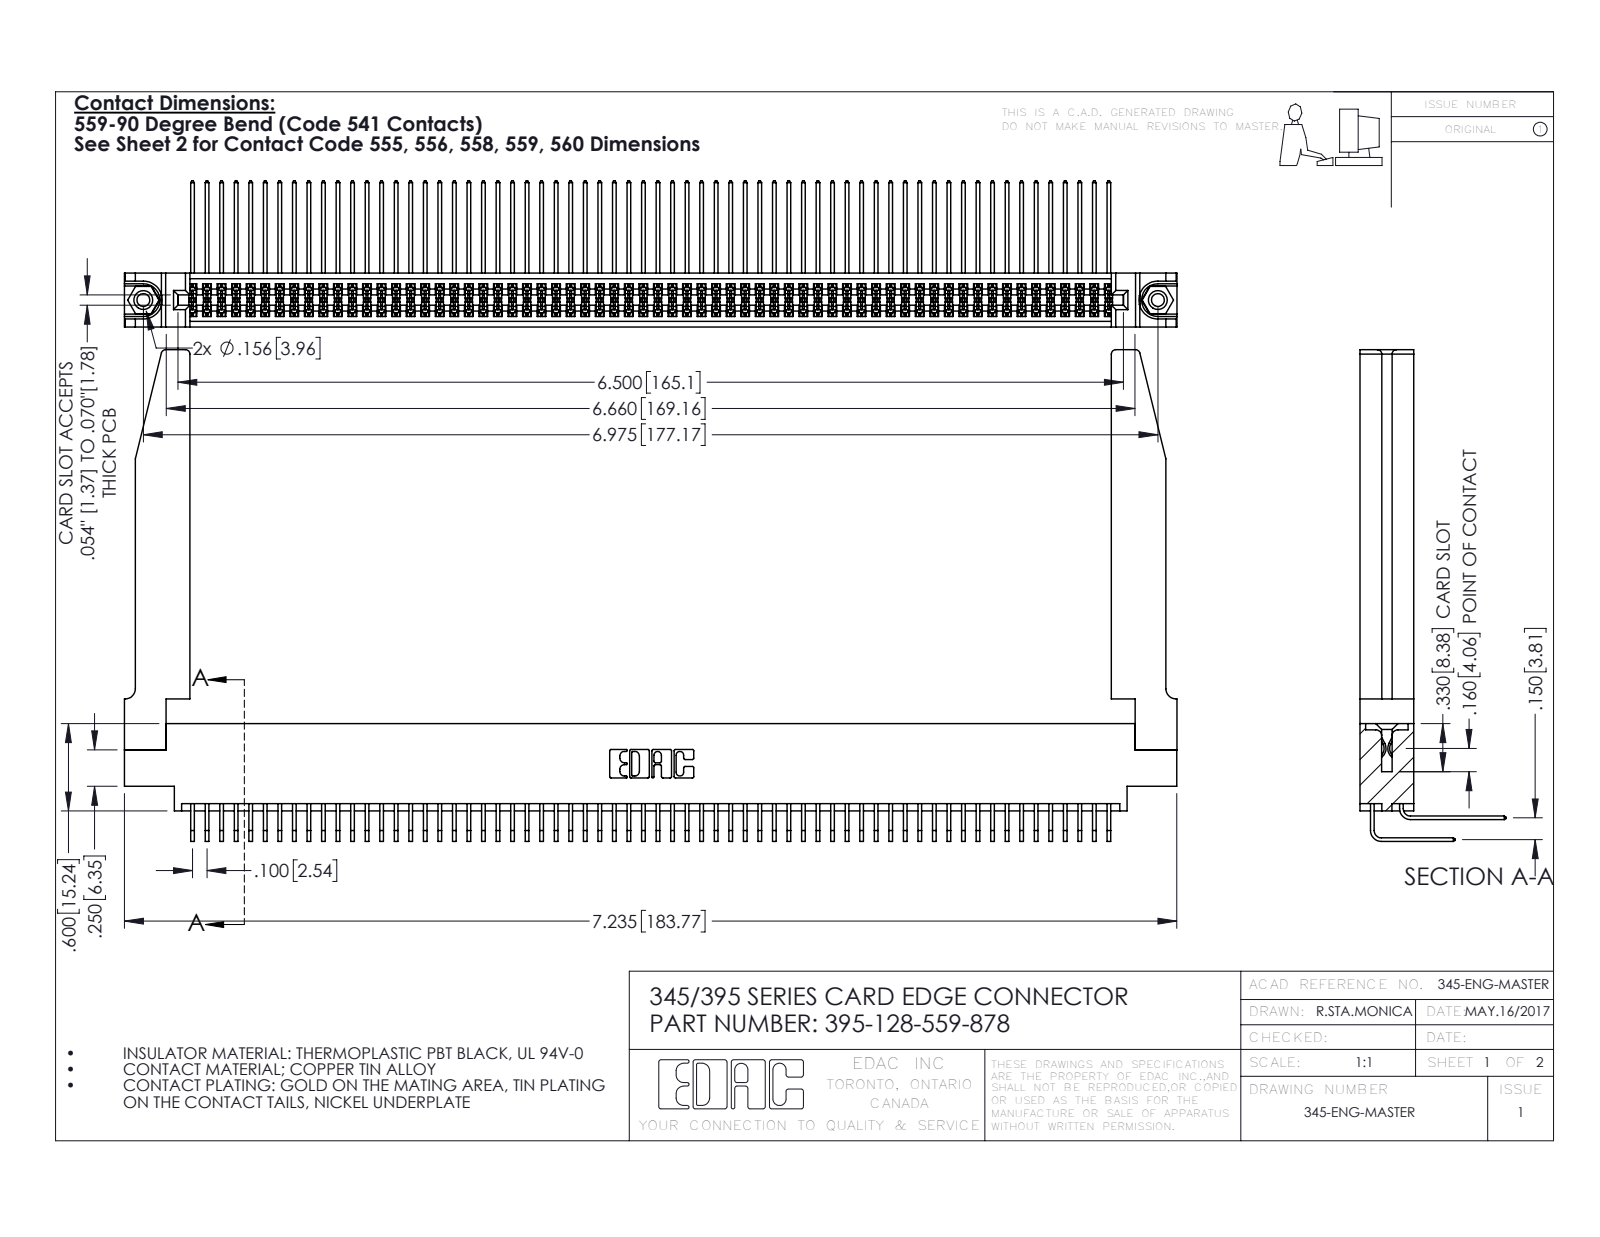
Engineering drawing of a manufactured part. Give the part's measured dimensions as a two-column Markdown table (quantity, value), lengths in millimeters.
| quantity | value |
| --- | --- |
| part name | 345-250-001_345-250-001-102; 345-292-001_559 Tail - 2; 345-220-078_345-220-078; 395-128-559-878 (+2 more) |
| STEP written by | SolidWorks 2016 (CONFIG_CONTROL_DESIGN) |
| units | millimeters |
| bodies | 133 solids, 7020 faces (4706 planar, 2262 cylindrical, 52 other) |
| overall size | 183.8 × 85.8 × 25.5 |
| volume | 26 450 mm³ |
| surface area | 38 500 mm² |
| round holes (diameter × count) | 2.3 × 2, 3.2 × 2, 4 × 2, 1.6 × 1 |
| round bosses / shafts (diameter × count) | 3.9 × 2 |
| partial cylindrical surfaces (radius × count) | 0.2 × 192, 0.3 × 22, 0.8 × 8, 0.2 × 6, 0.8 × 6, 0.7 × 3, 0.4 × 2, 0.5 × 2 |
| main face-to-face distances | 1.8, 7.6, 9.4, 2.5, 6.9, 0.6, 5.1, 5.7, 3.8, 4.4 |
| hole center spacings | 6.9, 171.2, 177.2 |
